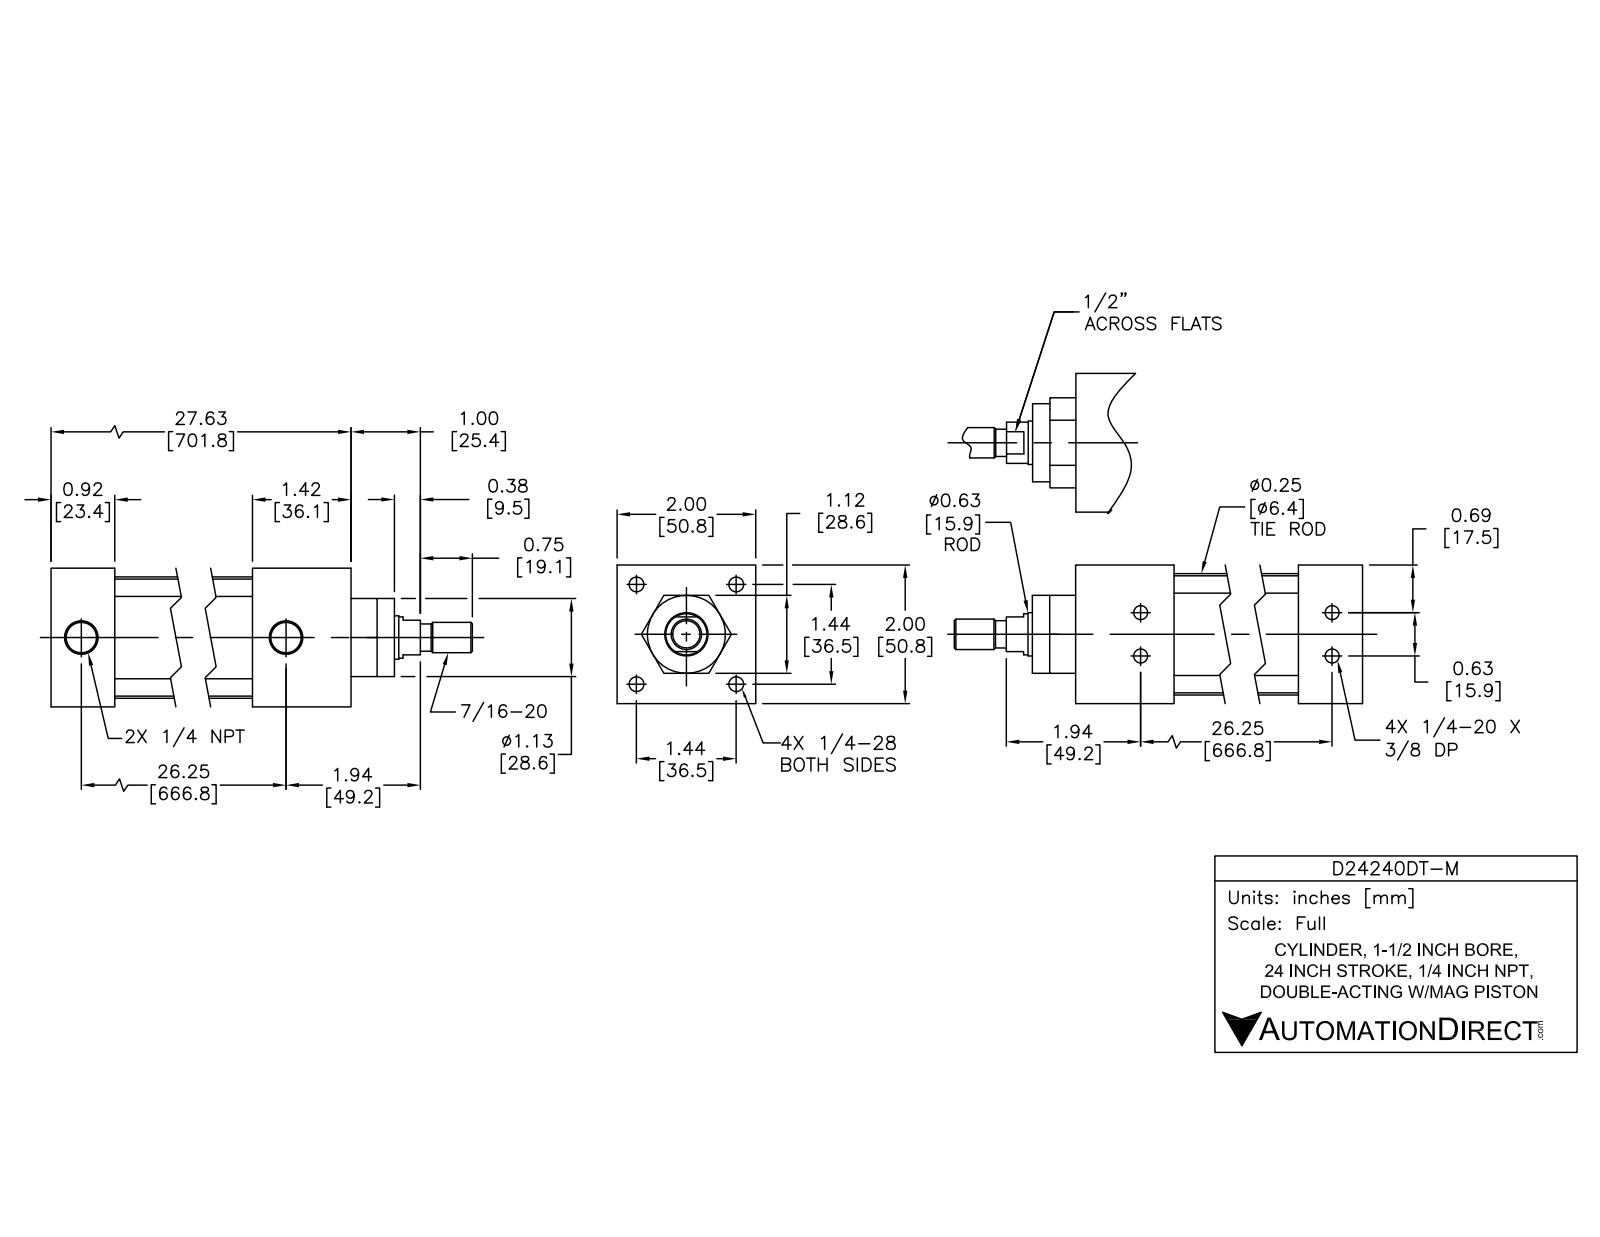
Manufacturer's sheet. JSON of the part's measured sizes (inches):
{"part_name": "D24240DT-M PISTON; D24240DT-M BODY; D24240DT-M", "step_written_by": "SolidWorks 2015 (AUTOMOTIVE_DESIGN)", "units": "inches", "bodies": {"solids": 12, "faces": 303, "planar": 99, "cylindrical": 114, "other": 90}, "overall_size": [29.371, 2, 2], "volume_in3": 39.01, "surface_area_in2": 452, "round_holes": [[0.196, 4], [0.211, 4], [0.281, 4], [0.406, 4], [0.297, 2], [0.477, 2], [0.625, 1], [0.628, 1], [1.5, 1]], "round_bosses_or_shafts": [[0.39, 4], [0.25, 4], [0.222, 4], [1.75, 1], [1.497, 1], [1.121, 1], [0.622, 1], [0.59, 1]], "partial_cylinders_radius": [[0.2, 4]], "face_to_face_distances": [2, 0.08, 25.201, 27.621, 1.42, 26.201, 26.701, 25.281, 0.92, 1.121], "hole_center_spacings": [0.313, 26.248, 0.625, 1.014, 1.014, 1.434, 1.434, 2.028]}
